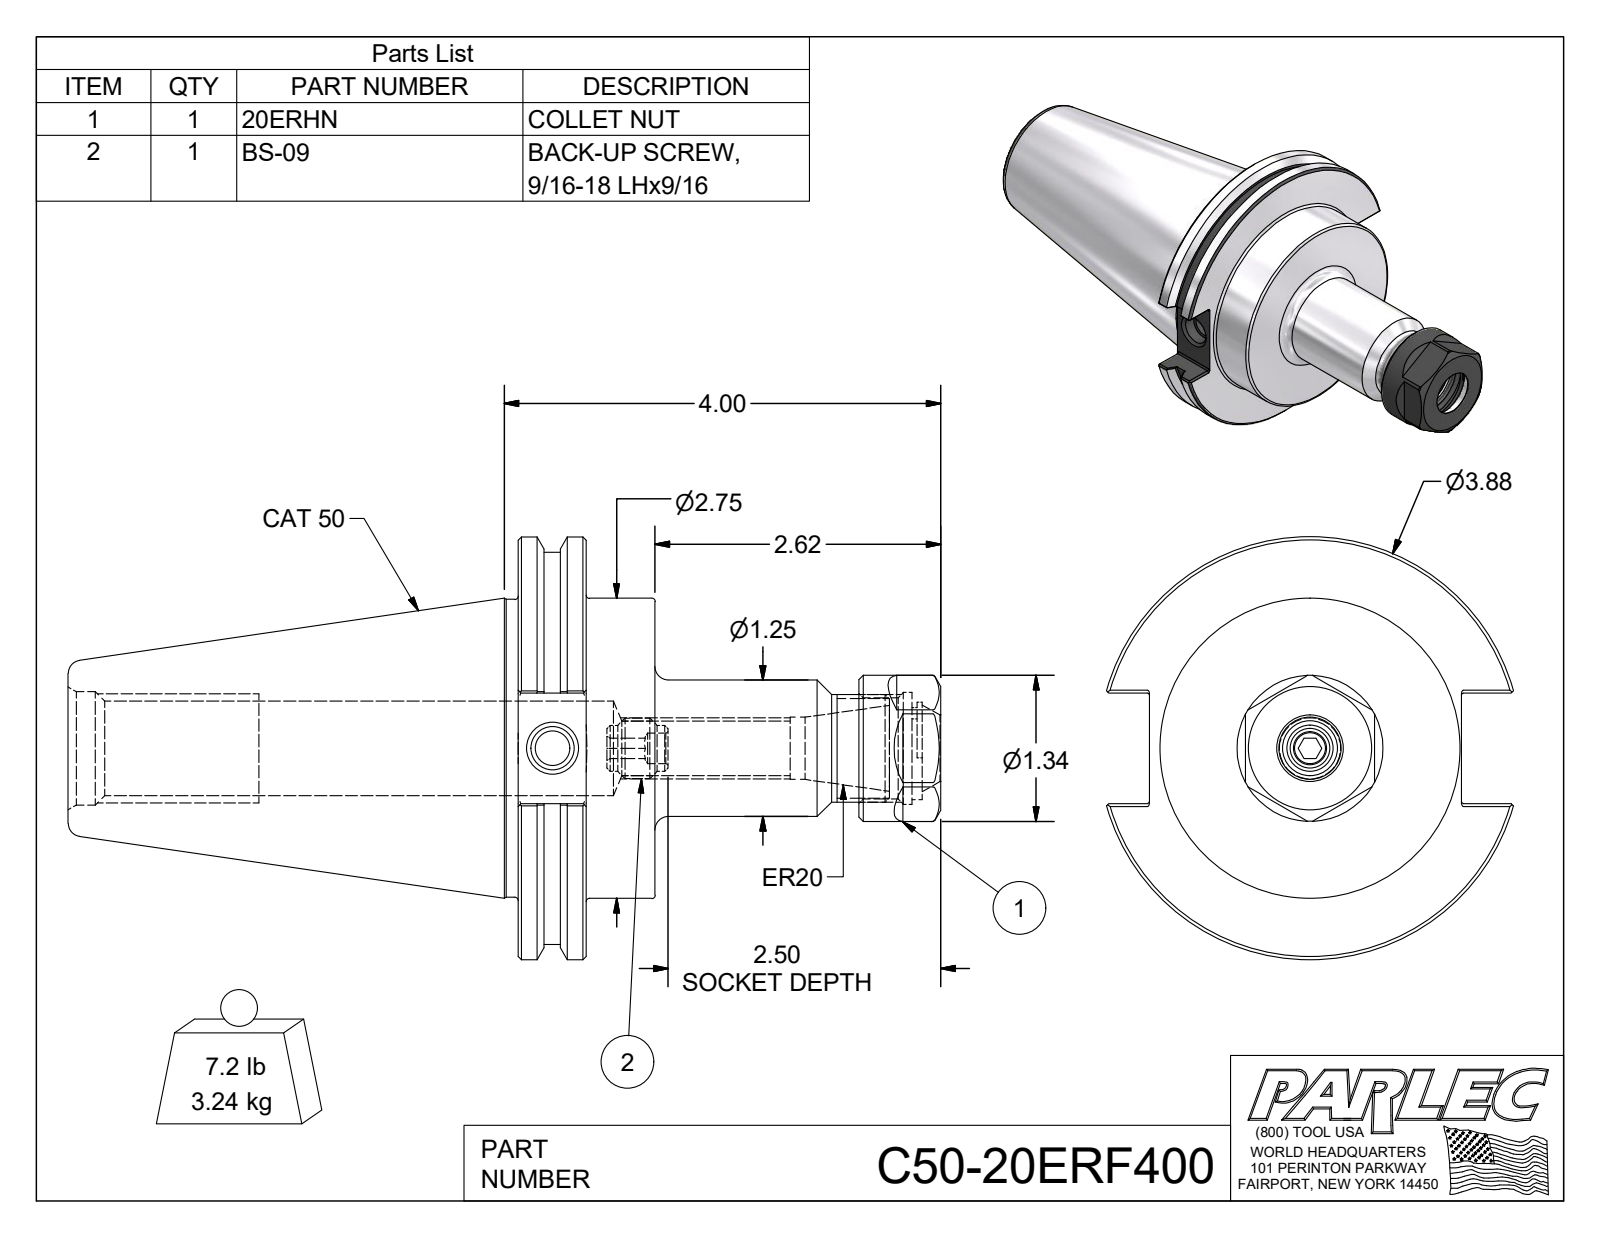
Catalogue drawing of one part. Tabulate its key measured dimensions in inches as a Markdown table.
| quantity | value |
| --- | --- |
| part name | C50-20ER4-1; 20ERHN; BS-09; C50-20ERF400 |
| STEP written by | Autodesk Inventor 2016 (AUTOMOTIVE_DESIGN) |
| units | inches |
| bodies | 3 solids, 152 faces (64 planar, 39 cylindrical, 49 other) |
| overall size | 8 × 3.875 × 3.729 |
| volume | 25.27 in³ |
| surface area | 94.94 in² |
| round holes (diameter × count) | 0.281 × 1, 0.315 × 1, 0.399 × 1, 0.502 × 1, 0.57 × 1, 0.61 × 1, 0.865 × 1, 0.925 × 1, 1.024 × 1, 1.038 × 1 |
| round bosses / shafts (diameter × count) | 3.875 × 1, 3.594 × 1, 2.75 × 1, 2.73 × 1, 1.339 × 1, 1.25 × 1, 0.984 × 1, 0.555 × 1 |
| partial cylindrical surfaces (radius × count) | 0.02 × 12, 0.373 × 1, 0.415 × 1, 0.423 × 1 |
| main face-to-face distances | 0.625, 1.255, 0.63, 3.875, 3.25, 2.62, 1.181, 4.125, 4.75, 5.38 |
